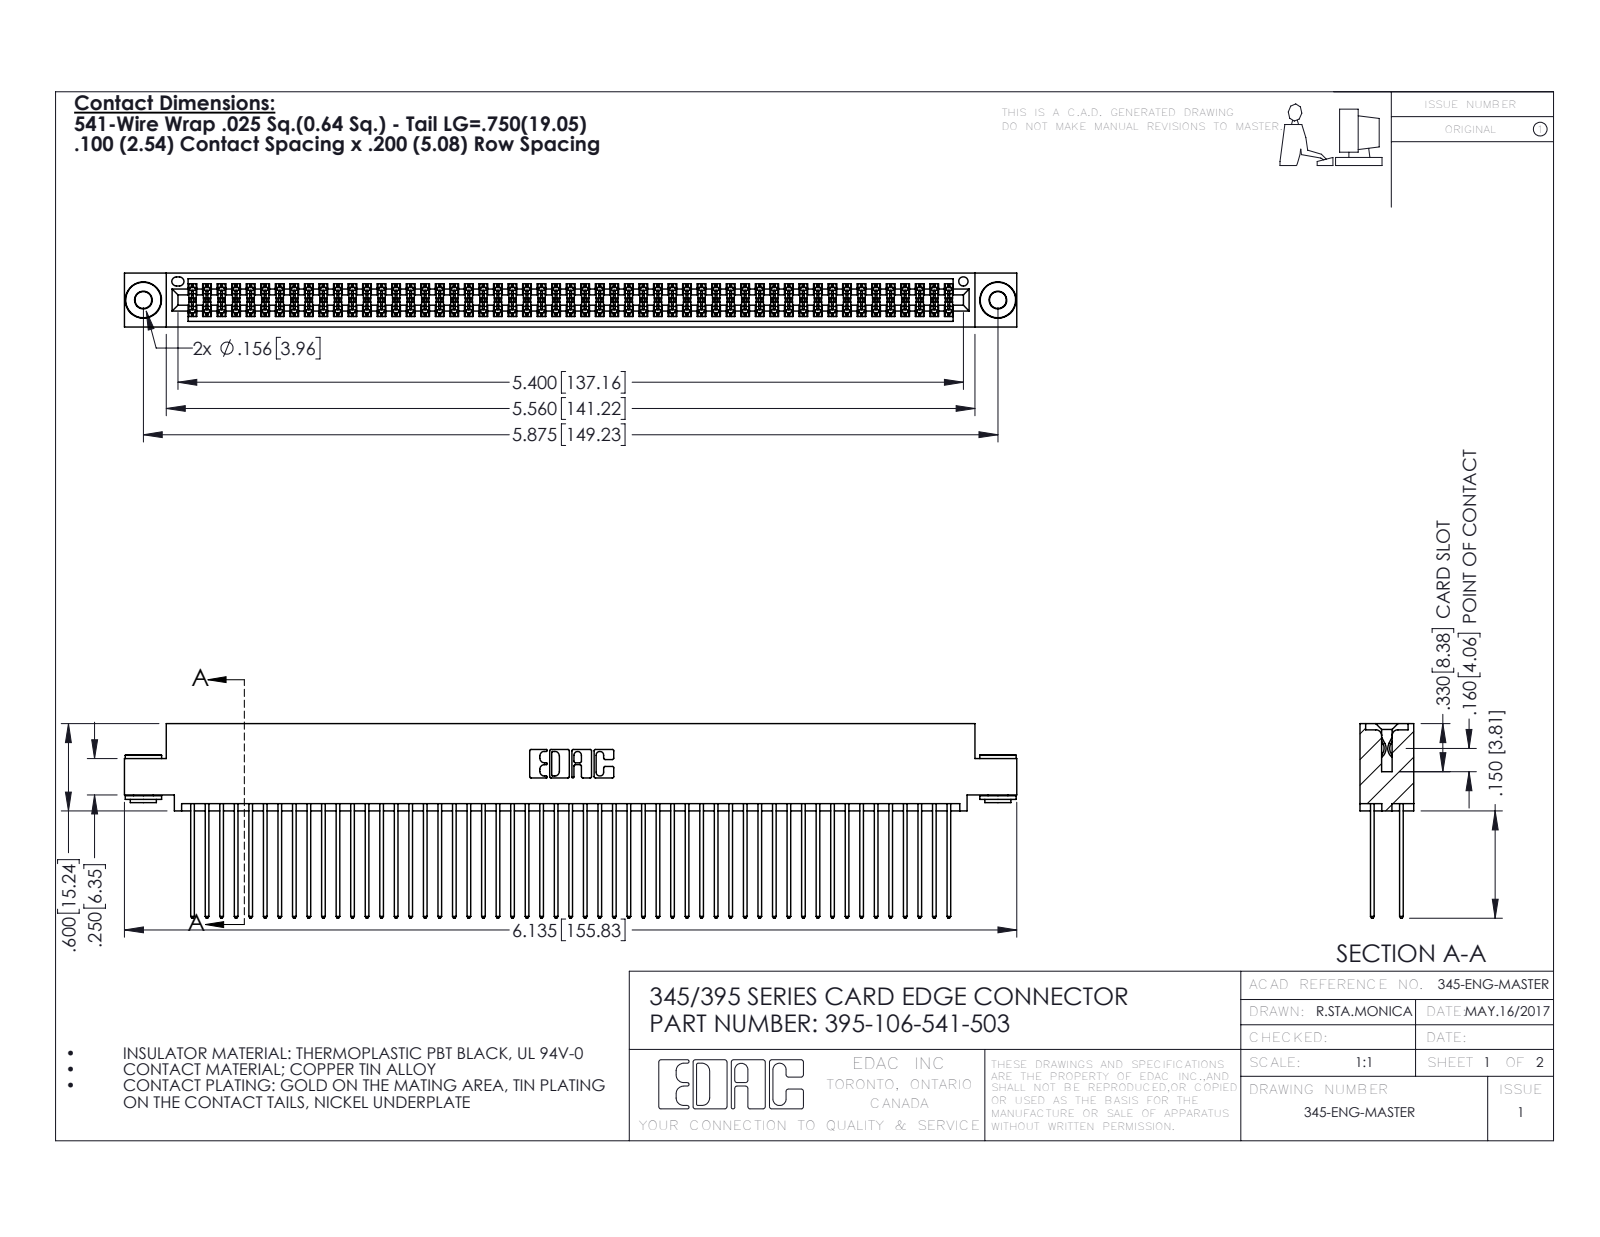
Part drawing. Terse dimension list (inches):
name: 345-292-001_345-293-141; 345-250-002_345-250-002-102; 395-106-541-503; 345 Part_0.110 Offset - 0.156 Dia-TH
written by: SolidWorks 2016 (CONFIG_CONTROL_DESIGN)
unit: in
bodies: 109 solids, 5468 faces (3592 planar, 1868 cylindrical, 8 other)
size: 6.135 × 1.337 × 0.37
volume: 0.964 in³; area: 41.41 in²
holes: 2× ⌀0.116, 2× ⌀0.156, 1× ⌀0.064
bosses: 2× ⌀0.25, 2× ⌀0.18, 2× ⌀0.136
rounds: 159× R0.006, 106× R0.01, 22× R0.01, 6× R0.007, 6× R0.031, 3× R0.026, 2× R0.014, 2× R0.019
face distances: 0.072, 0.298, 0.2, 0.025, 0.098, 0.272, 0.225, 0.37, 0.175, 0.149
hole spacings: 0.27, 5.639, 5.875
